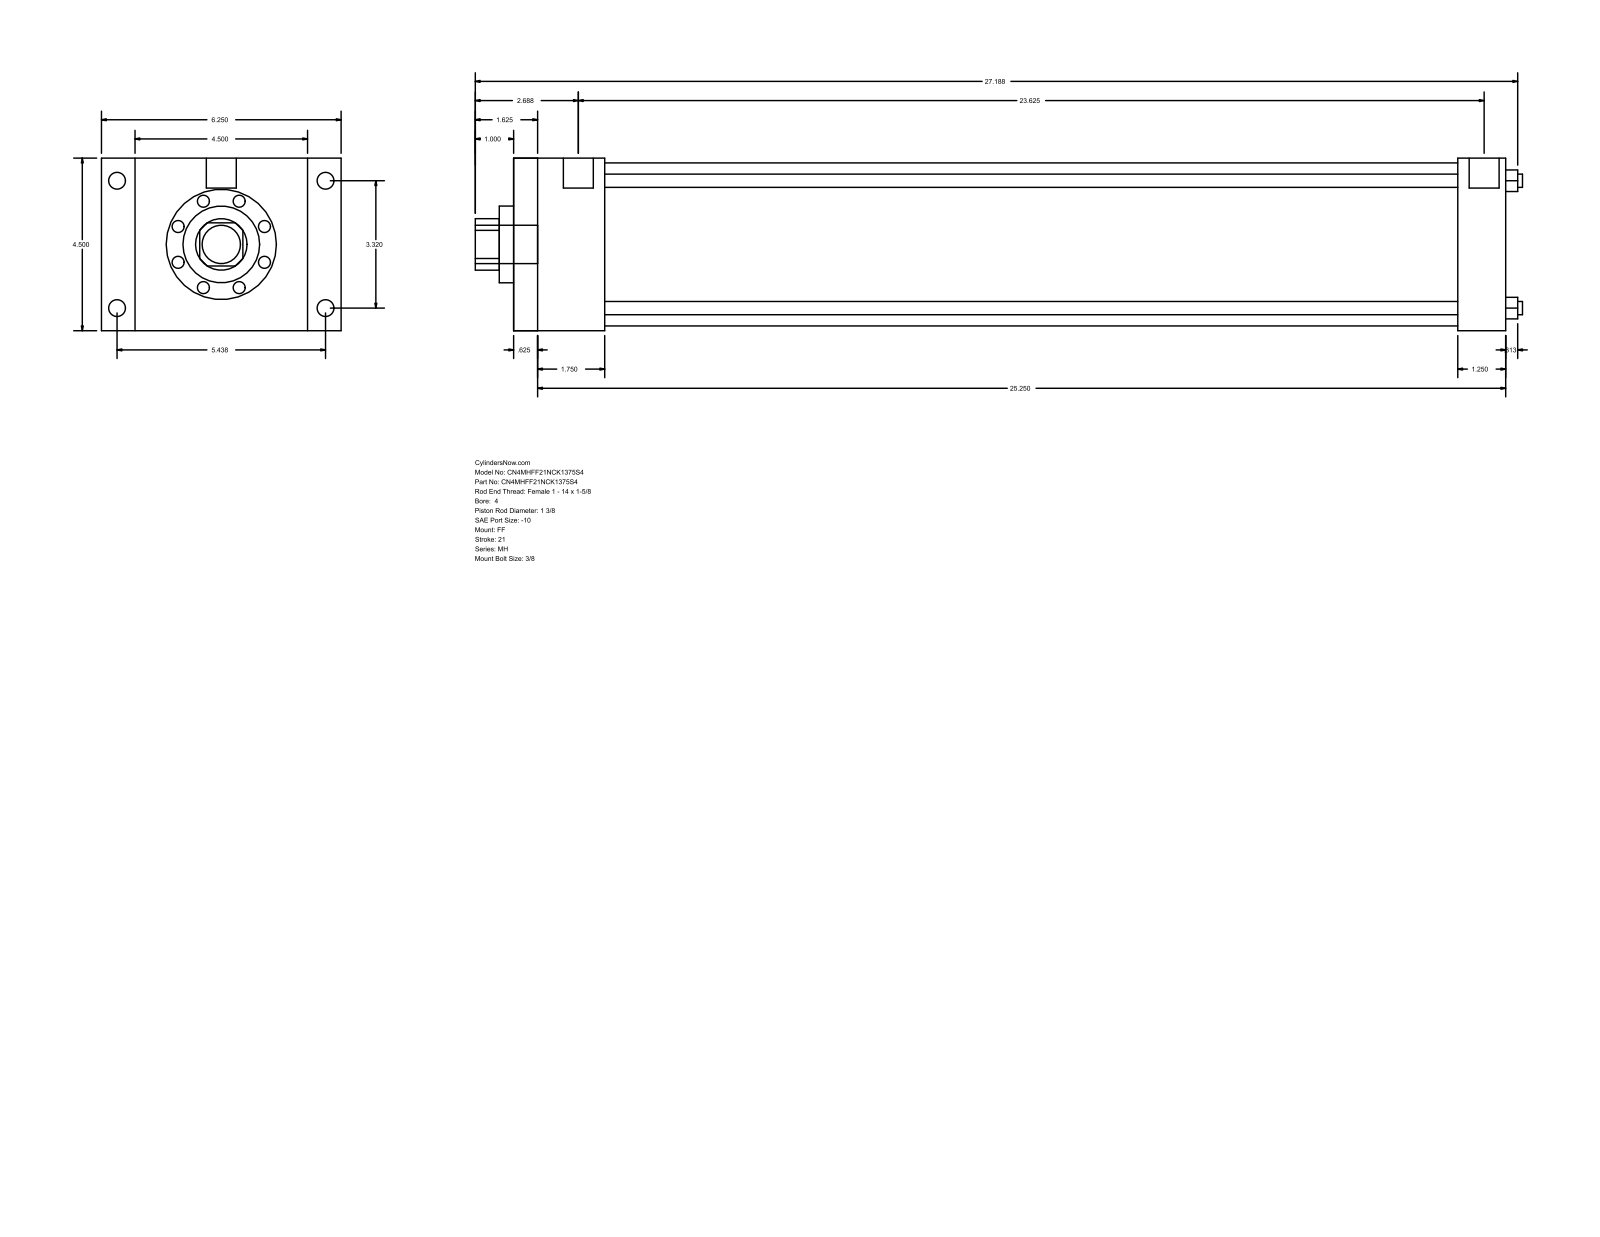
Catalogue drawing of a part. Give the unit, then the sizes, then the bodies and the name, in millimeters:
Units: millimetres
Overall size (bounding box): 693.74 × 158.75 × 114.3
Round holes (diameter × count): ⌀8.76 ×4, ⌀34.92 ×1, ⌀50.8 ×1, ⌀107.95 ×1
Round bosses / shafts (diameter × count): ⌀11.13 ×4, ⌀8.73 ×4, ⌀19.84 ×2, ⌀25.4 ×1
Partial cylindrical surfaces — rounded edges, fillets, slot ends (radius × count): R17.06 ×1
Main face-to-face distances: 114.3, 657.22, 15.87, 641.35, 60.32, 44.45, 596.9, 625.48, 609.61, 565.16
Hole centre spacings: 59.62, 84.32, 119.25
Bodies: 0 solids, 92 faces (64 planar, 28 cylindrical, 0 other)
Part name (STEP PRODUCT): MH_FF__0400_1.375
STEP written by: GSSL Pune (CONFIG_CONTROL_DESIGN)
